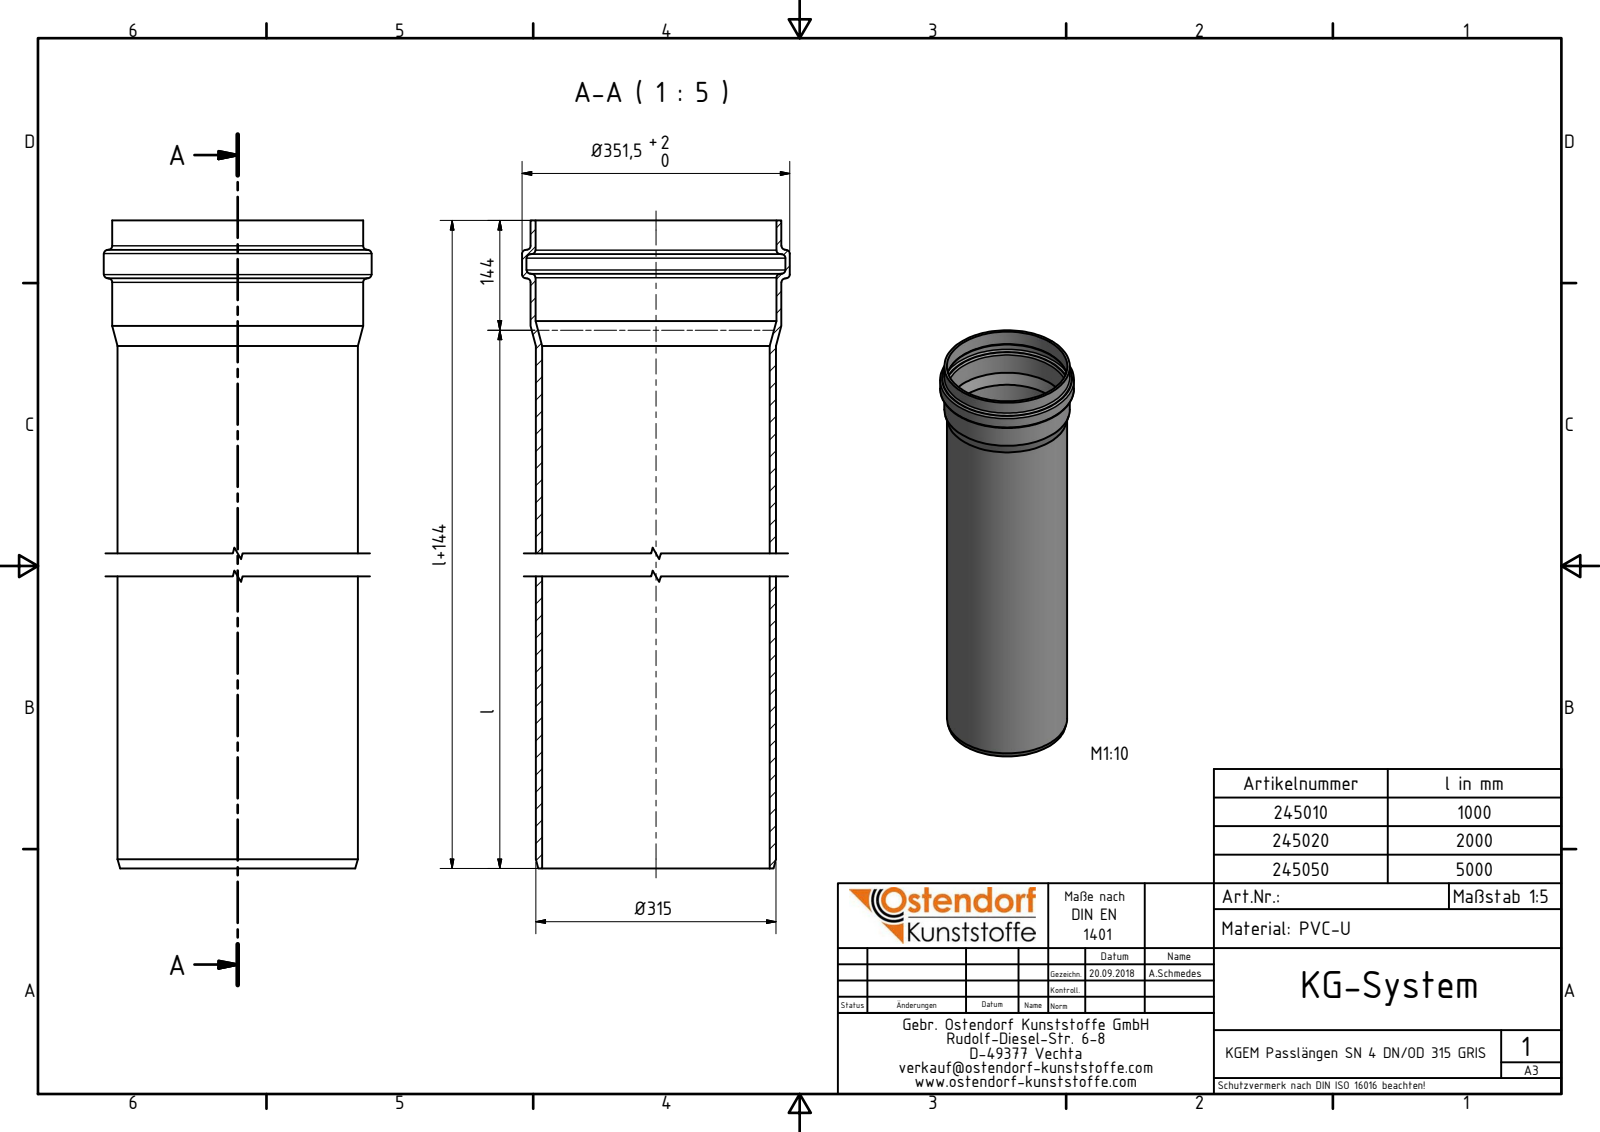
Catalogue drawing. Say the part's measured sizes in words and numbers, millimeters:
The part is named "245050 KGEM Passlängen SN 4 DN_OD 315x5000 GRIS". Its 3-D file was written by "Autodesk Inventor 2016 (AUTOMOTIVE_DESIGN)". It is 1 solid with 25 faces: 2 planar, 8 cylindrical and 15 other. Overall it measures 5144 by 351.5 by 351.5 millimeters. Its volume is 40 640 000 cubic millimeters and its surface area 9 988 000 square millimeters. Round holes: 1 of diameter 298.9, 1 of diameter 316.35, 1 of diameter 339.9. Round bosses or shafts: 1 of diameter 351.5, 1 of diameter 329.35, 1 of diameter 315.3. The main face-to-face distances are 5144.
